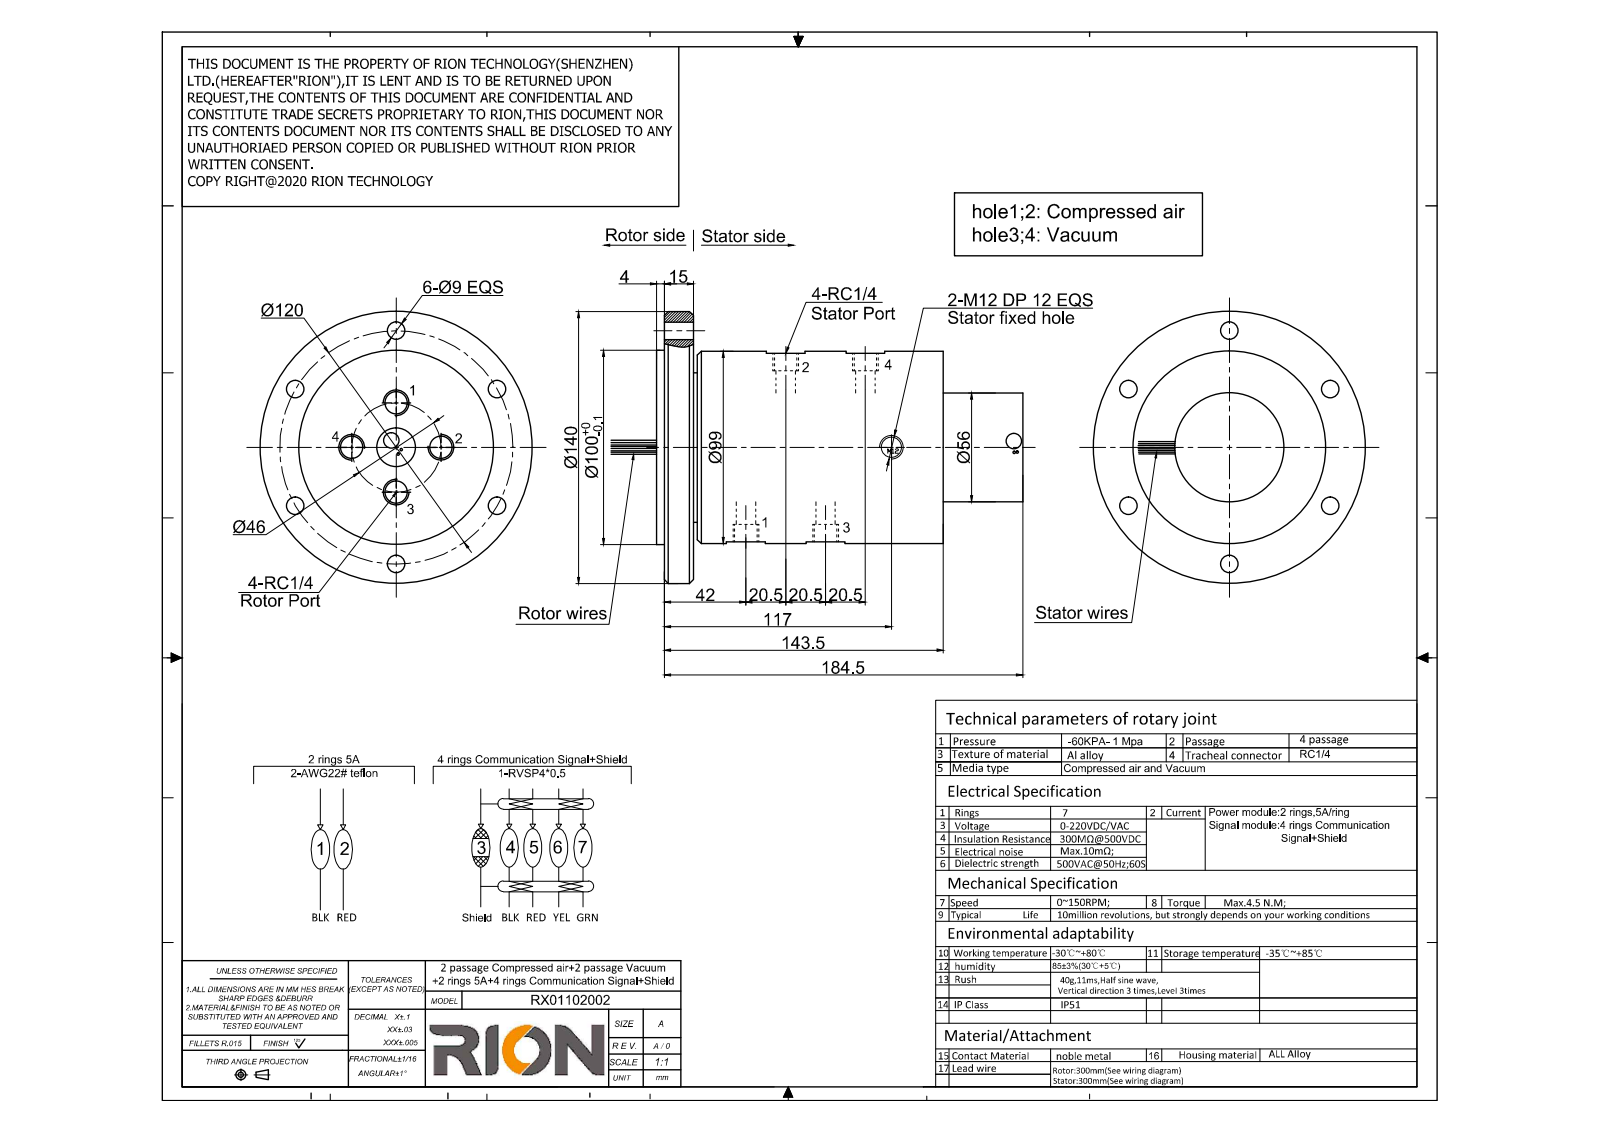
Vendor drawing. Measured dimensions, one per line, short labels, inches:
name: RX01102002
written by: SolidWorks 2014 (AUTOMOTIVE_DESIGN)
unit: in
bodies: 1 solid, 131 faces (33 planar, 56 cylindrical, 42 other)
size: 8.563 × 5.512 × 5.512
volume: 80.49 in³; area: 156.6 in²
holes: 8× ⌀0.438, 6× ⌀0.354, 1× ⌀0.402, 1× ⌀0.787
bosses: 4× ⌀0.051, 2× ⌀0.315, 1× ⌀5.512, 1× ⌀3.937, 1× ⌀3.898, 1× ⌀3.031, 1× ⌀2.205
face distances: 0.748, 0.591, 0.157, 5.807, 5.65, 5.059, 1.614, 7.421, 7.264, 6.673
hole spacings: 2.362, 4.091, 0.906, 1.281, 1.642, 2.064, 2.53, 2.922
